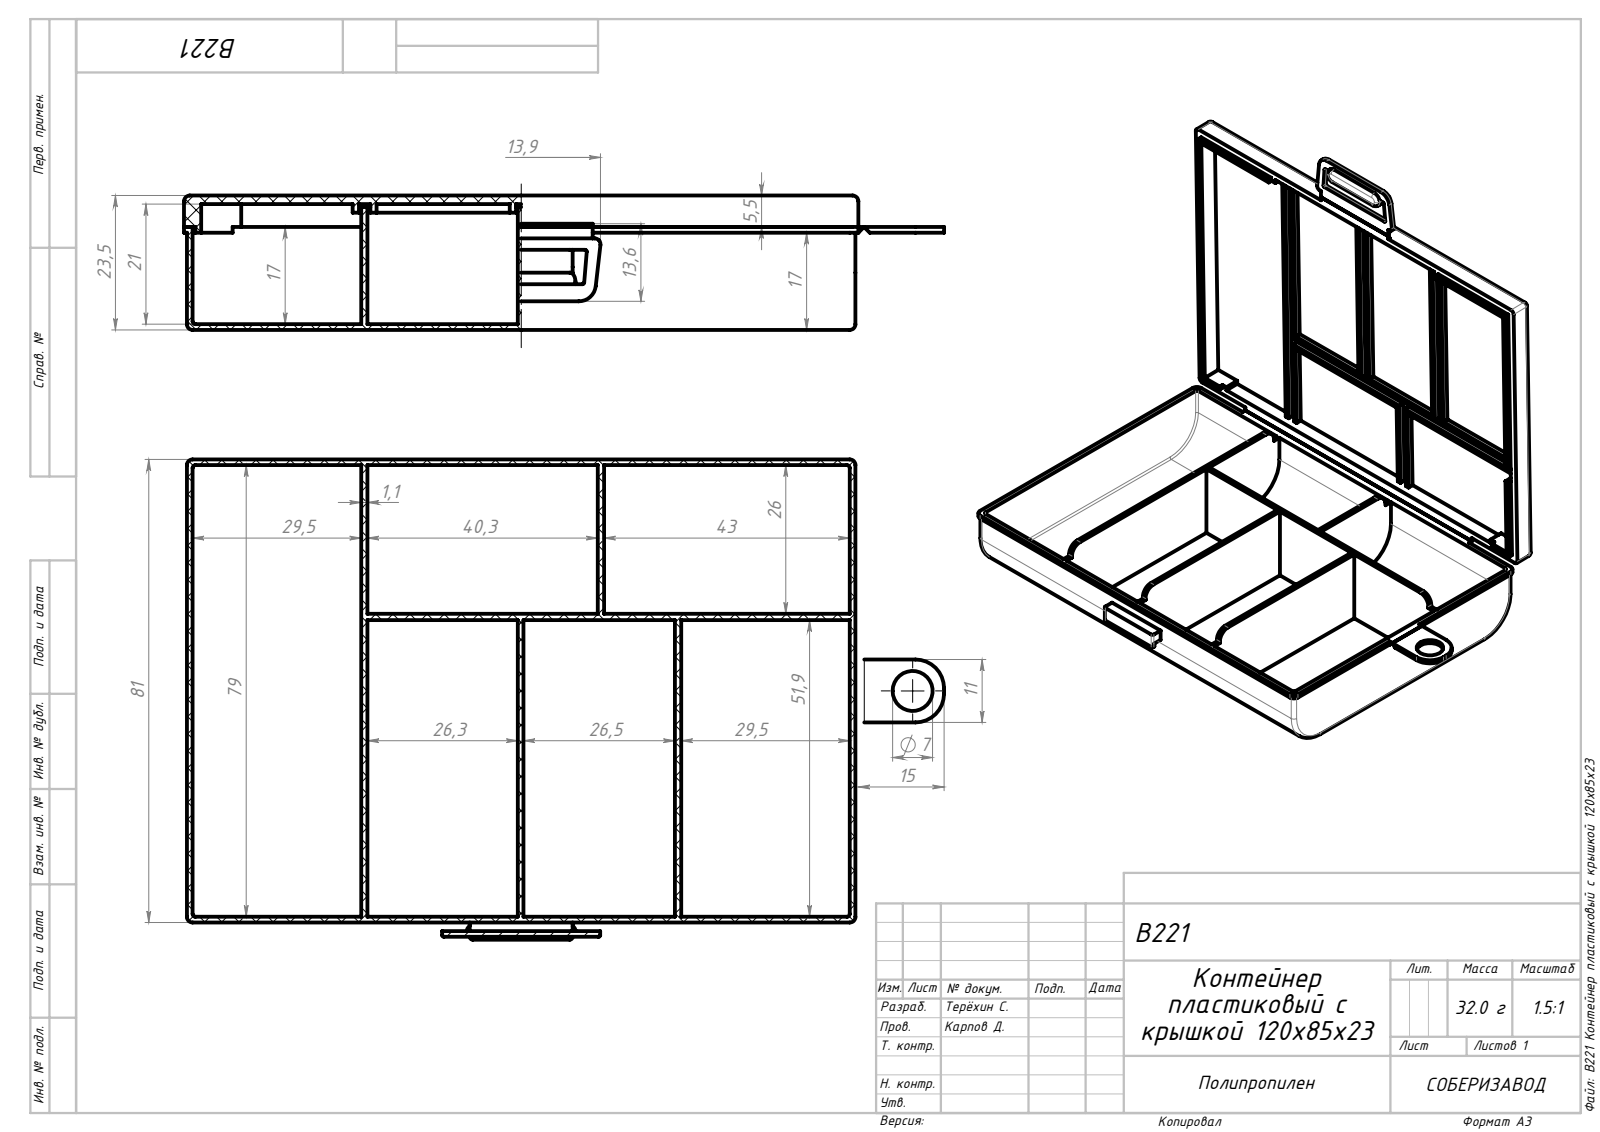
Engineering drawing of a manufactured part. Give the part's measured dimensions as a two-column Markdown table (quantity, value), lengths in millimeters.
| quantity | value |
| --- | --- |
| part name | B221 Емкость_00; B221 Крышка_00; B221 Защелка_00; B221 Контейнер пластиковый с крышкой 120x85x23 (+1 more) |
| STEP written by | SolidWorks 2021 (AUTOMOTIVE_DESIGN) |
| units | millimeters |
| bodies | 4 solids, 259 faces (168 planar, 69 cylindrical, 22 other) |
| overall size | 133 × 85.5 × 23.5 |
| volume | 42 717 mm³ |
| surface area | 68 674 mm² |
| round holes (diameter × count) | 7 × 1 |
| partial cylindrical surfaces (radius × count) | 1 × 18, 0.3 × 11, 0.5 × 8, 3 × 5, 1.5 × 4, 10 × 4, 2 × 2, 5 × 2 |
| main face-to-face distances | 1.5, 1, 22, 23.5, 21, 22.5, 1.1, 0.5, 116, 85.4 |
